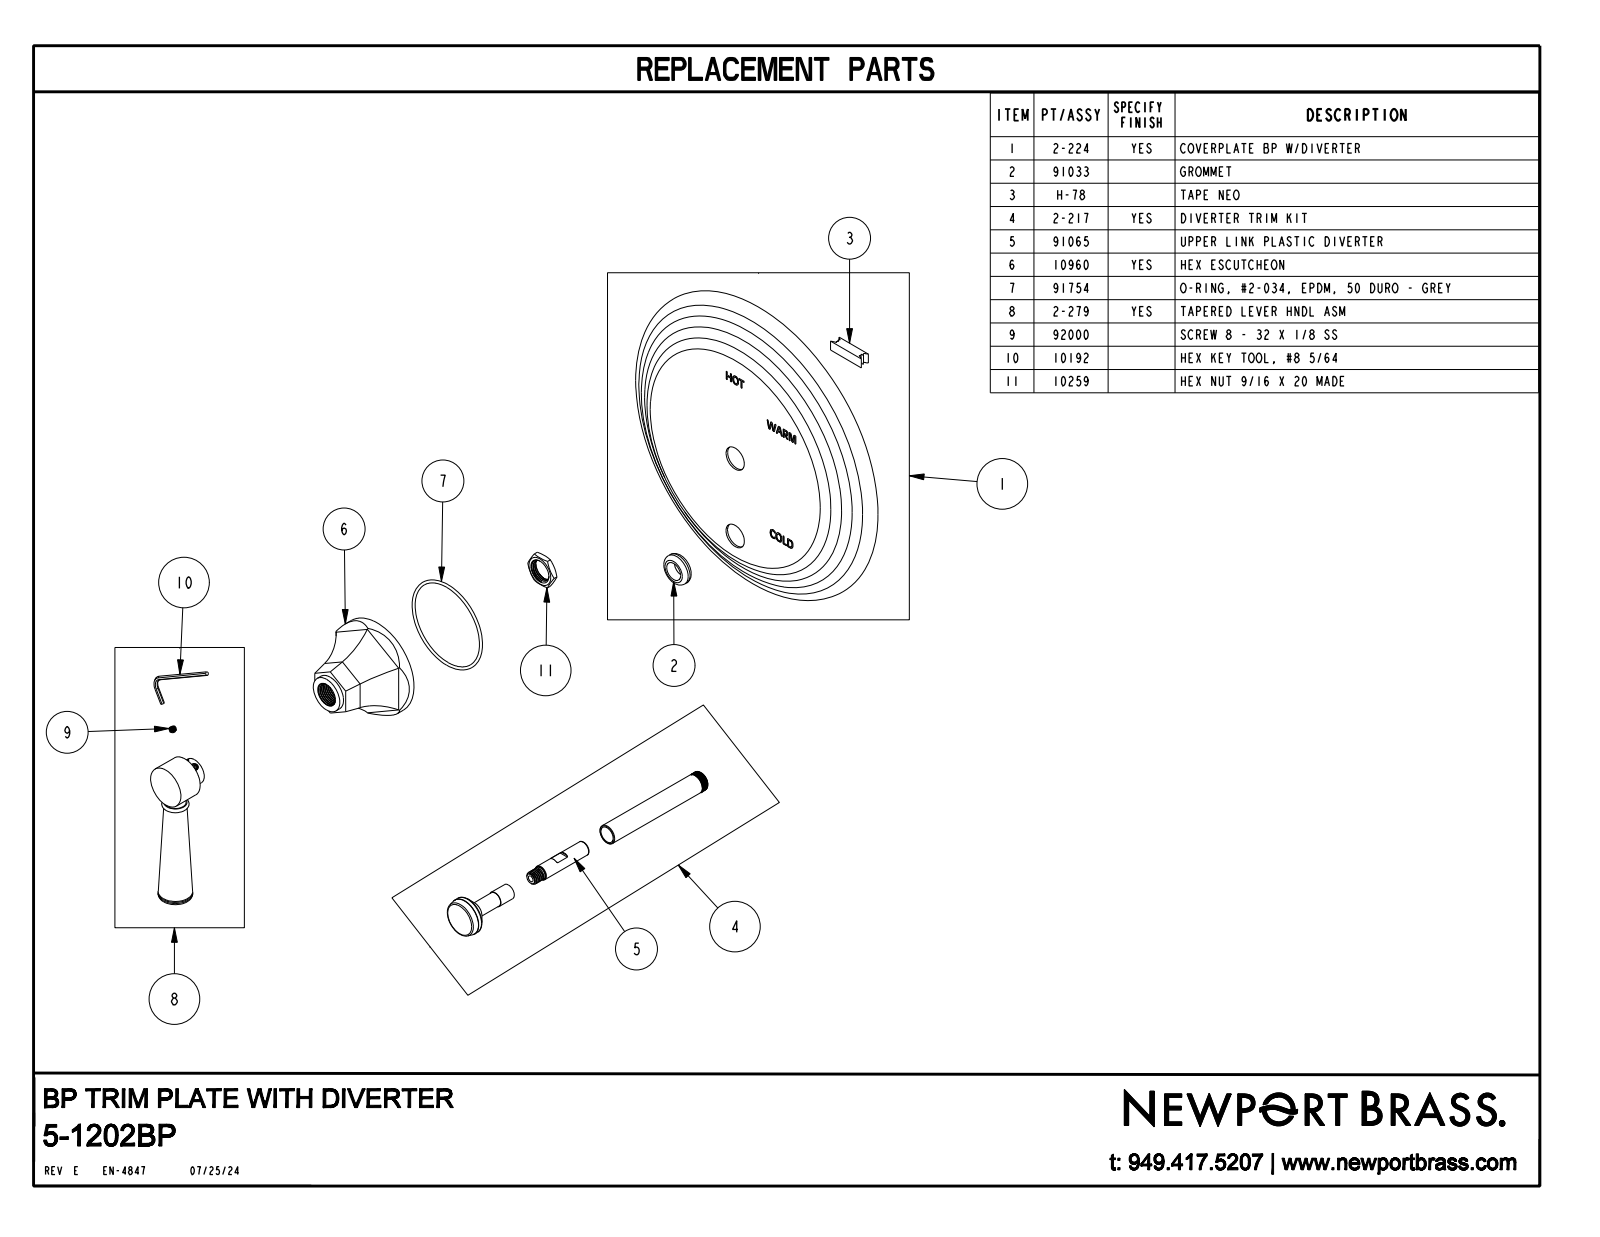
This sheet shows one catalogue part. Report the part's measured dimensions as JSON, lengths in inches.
{"part_name": "5-1202BP", "step_written_by": "CREO PARAMETRIC BY PTC INC, 2018400 (CONFIG_CONTROL_DESIGN)", "units": "inches", "bodies": {"solids": 1, "faces": 253, "planar": 121, "cylindrical": 26, "other": 106}, "overall_size": [7.75, 7.75, 3.42], "volume_in3": 33, "surface_area_in2": 120.4, "round_holes": [[0.385, 1]], "round_bosses_or_shafts": [[2.375, 1], [0.98, 1], [0.9, 1], [0.86, 1], [0.792, 1], [0.625, 1], [0.472, 1], [0.365, 1]], "partial_cylinders_radius": [[1.541, 6]], "face_to_face_distances": [0.754, 2.286, 1.532, 2.711, 1.957, 0.425, 2.281, 1.527, 0.43, 2.401]}
